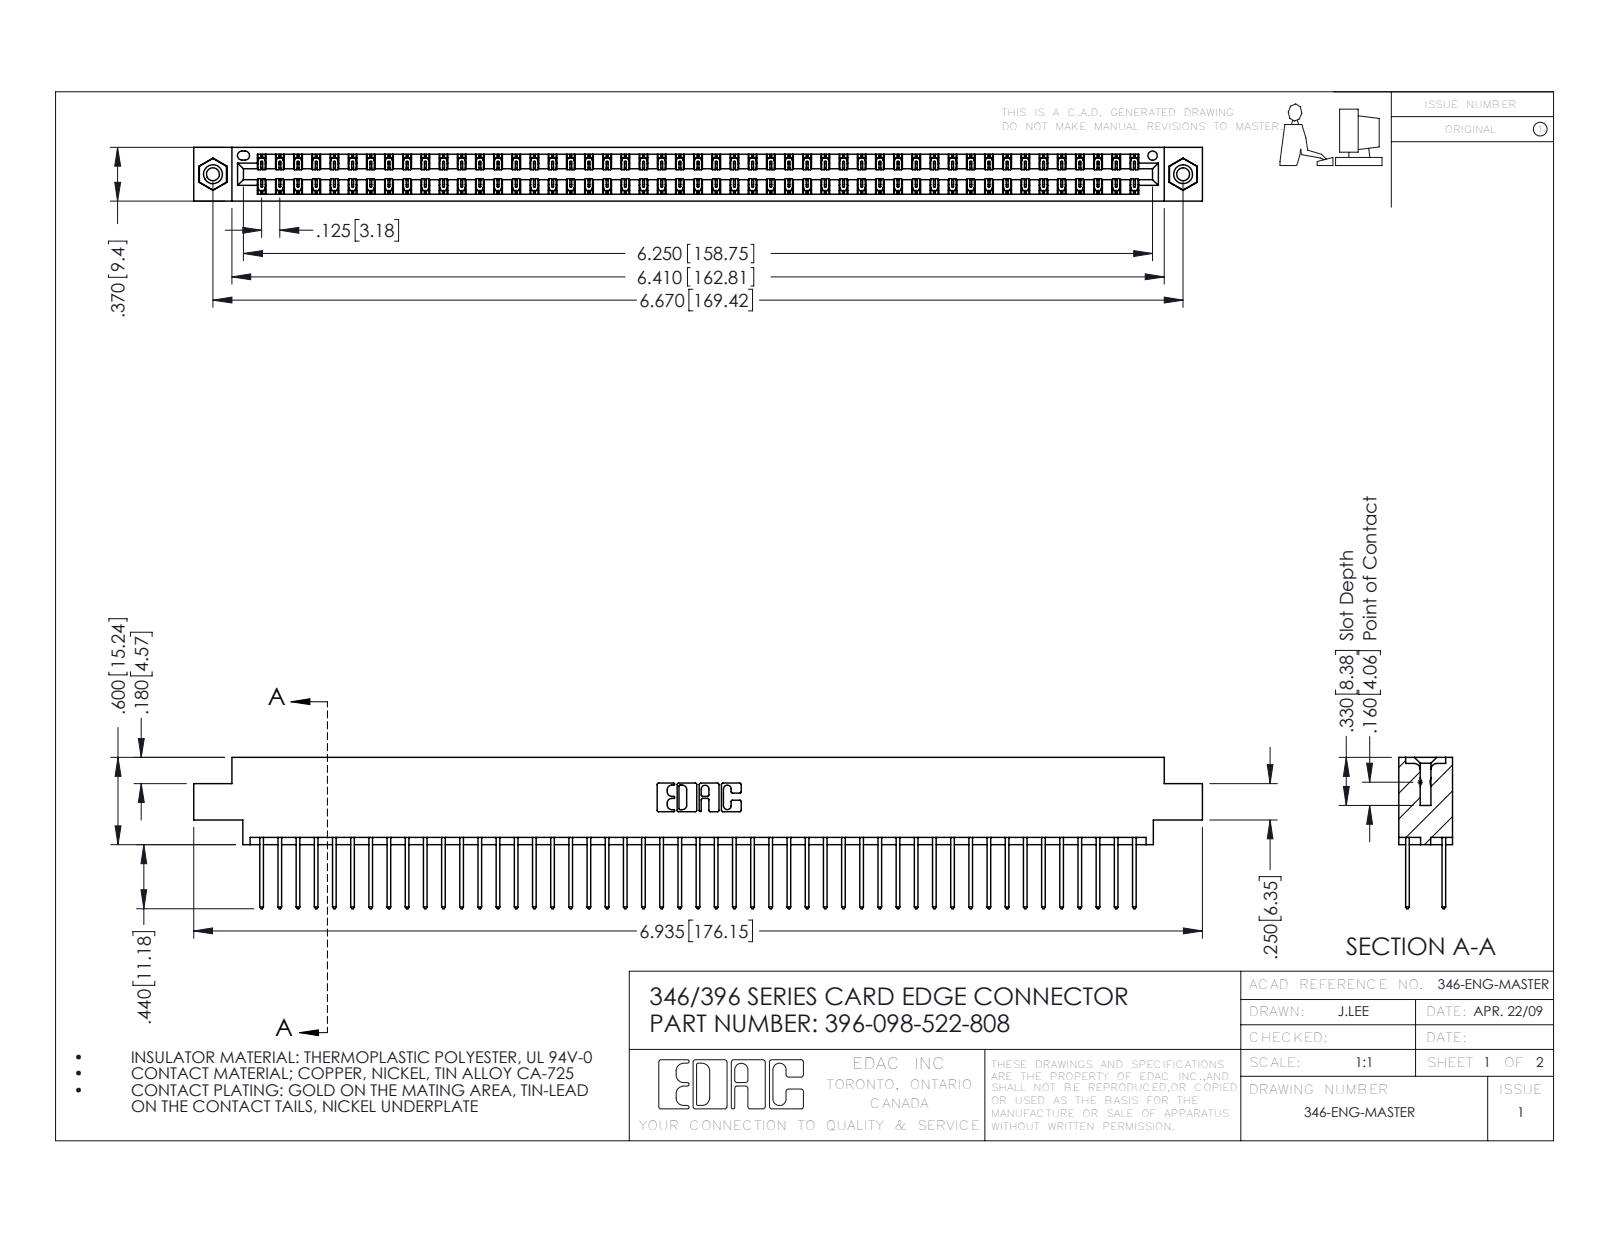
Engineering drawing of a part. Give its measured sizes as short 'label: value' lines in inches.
name: 345-250-001_345-250-003-102; 346 Part_0.170 Offset - 0.156 Dia-TI; 396-098-522-808; 345-292-001_345-293-122
written by: SolidWorks 2016 (CONFIG_CONTROL_DESIGN)
unit: in
bodies: 101 solids, 5282 faces (3542 planar, 1724 cylindrical, 16 other)
size: 6.935 × 1.04 × 0.37
volume: 1.057 in³; area: 39.19 in²
holes: 2× ⌀0.089, 2× ⌀0.125, 2× ⌀0.156, 1× ⌀0.064
bosses: 2× ⌀0.155
rounds: 147× R0.006, 98× R0.01, 22× R0.01, 6× R0.007, 6× R0.031, 3× R0.026, 2× R0.014, 2× R0.022
face distances: 0.048, 0.322, 0.25, 0.37, 0.072, 0.298, 0.025, 0.275, 0.222, 0.148
hole spacings: 0.246, 6.461, 6.67
